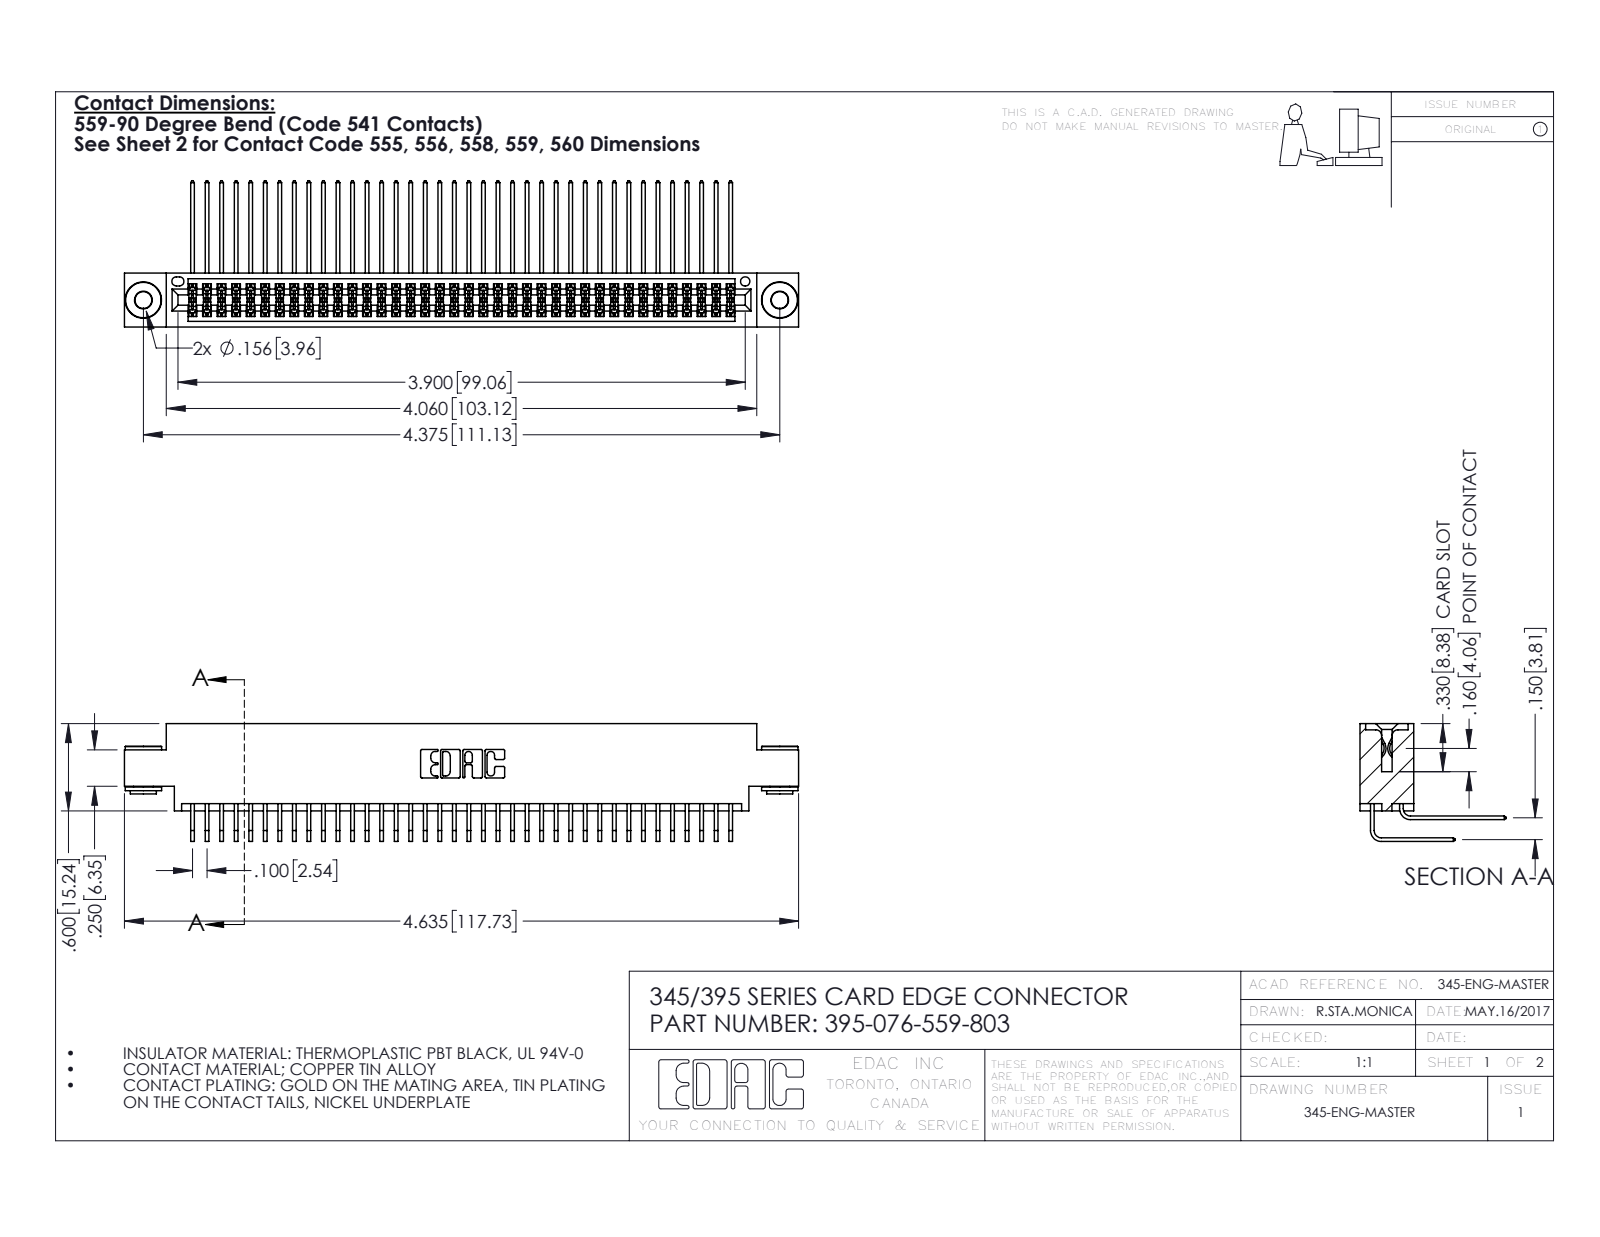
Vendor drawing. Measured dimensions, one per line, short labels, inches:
name: 395-076-559-803; 345-292-001_558 559 Tail - 1; 345-292-001_559 Tail - 2; 345-250-002_345-250-002-102 (+1 more)
written by: SolidWorks 2016 (CONFIG_CONTROL_DESIGN)
unit: in
bodies: 79 solids, 4120 faces (2754 planar, 1358 cylindrical, 8 other)
size: 4.635 × 1.005 × 0.809
volume: 0.717 in³; area: 30.52 in²
holes: 2× ⌀0.116, 2× ⌀0.156, 1× ⌀0.064
bosses: 2× ⌀0.25, 2× ⌀0.18, 2× ⌀0.136
rounds: 114× R0.006, 22× R0.01, 6× R0.007, 6× R0.031, 3× R0.026, 2× R0.014, 2× R0.019, 2× R0.022
face distances: 0.072, 0.298, 0.37, 0.2, 0.098, 0.272, 0.025, 0.175, 0.225, 0.15
hole spacings: 0.27, 4.139, 4.375
